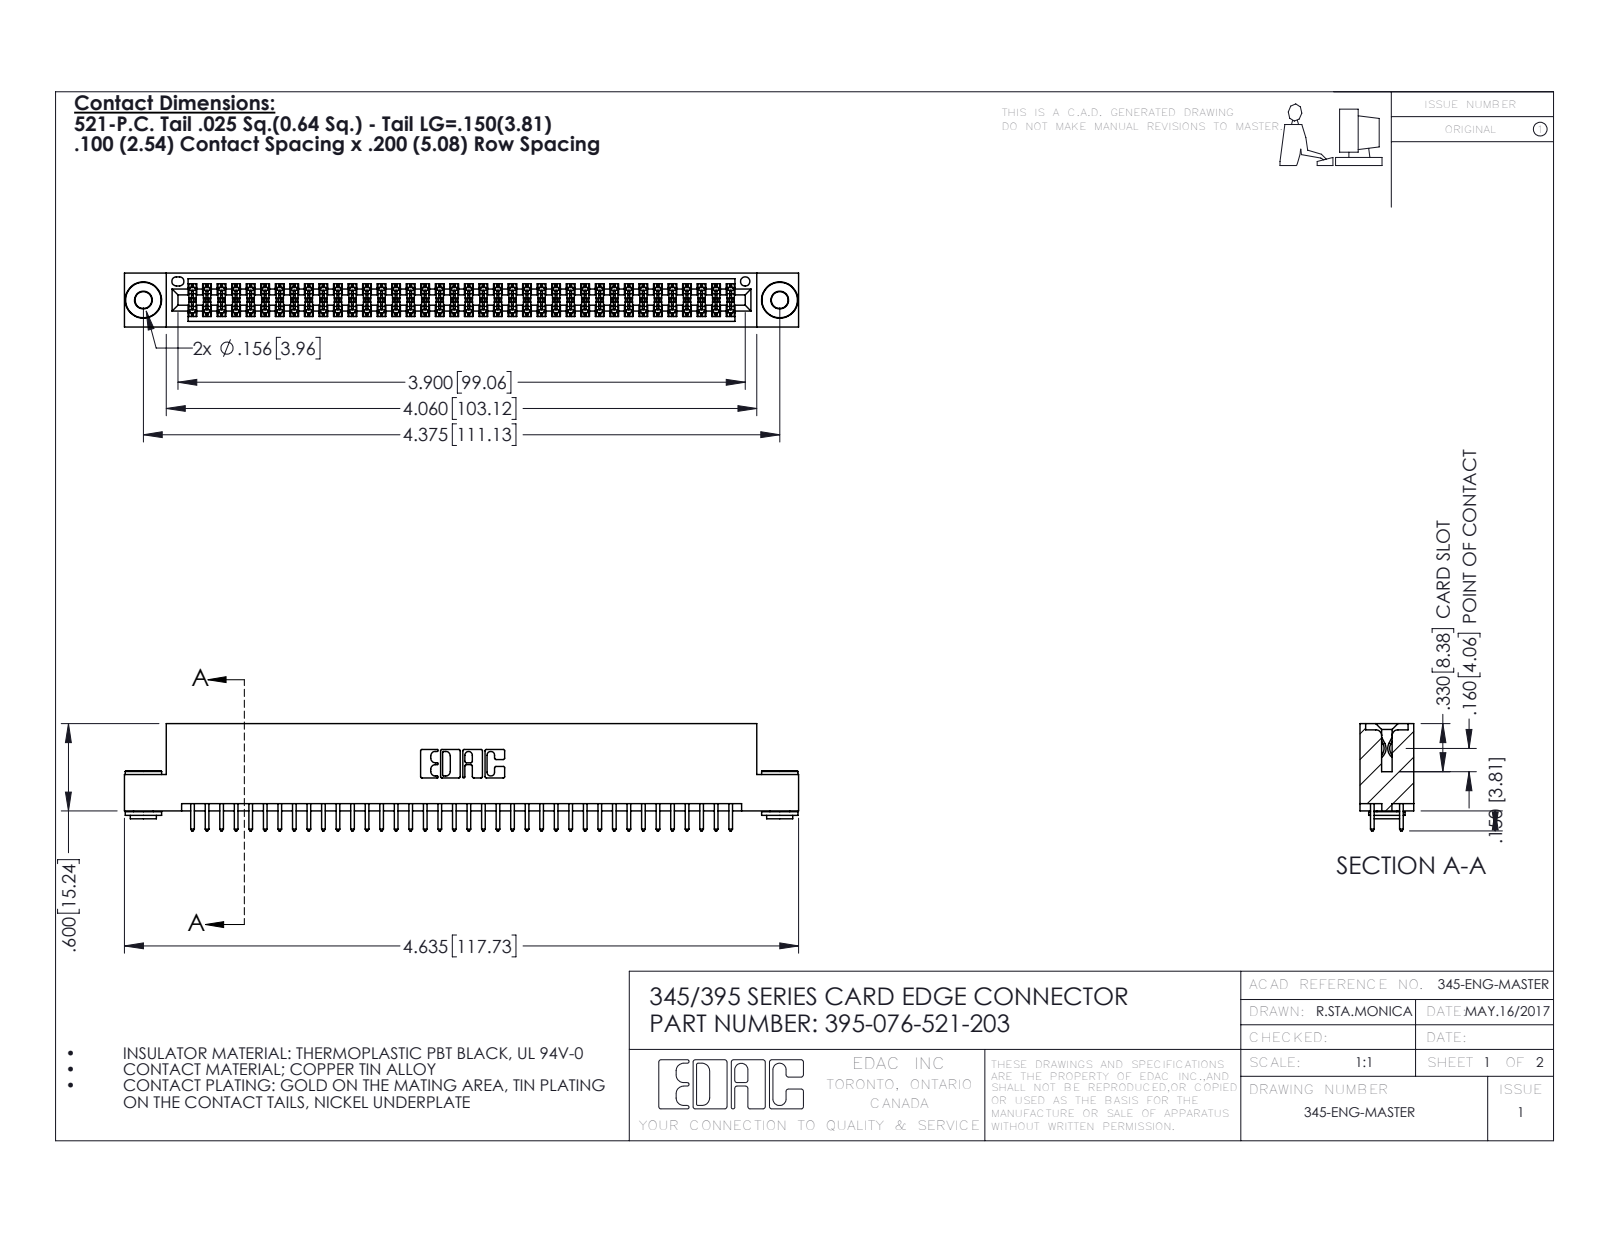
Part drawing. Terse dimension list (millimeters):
name: 395-076-521-203; 345 Part_Flush Mounting Lugs - 0.156 Dia-TH; 345-292-001_345-293-121; 345-250-002_345-250-002-102
written by: SolidWorks 2016 (CONFIG_CONTROL_DESIGN)
unit: mm
bodies: 79 solids, 3964 faces (2598 planar, 1358 cylindrical, 8 other)
size: 117.7 × 18.7 × 9.4
volume: 11 400 mm³; area: 16 760 mm²
holes: 2× ⌀2.9, 2× ⌀4, 1× ⌀1.6
bosses: 2× ⌀6.4, 2× ⌀4.6, 2× ⌀3.5
rounds: 114× R0.2, 76× R0.3, 22× R0.3, 6× R0.2, 6× R0.8, 3× R0.7, 2× R0.4, 2× R0.5
face distances: 1.8, 7.6, 5.1, 9.4, 0.6, 2.5, 6.9, 5.7, 4.4, 3.8
hole spacings: 6.9, 105.1, 111.1
